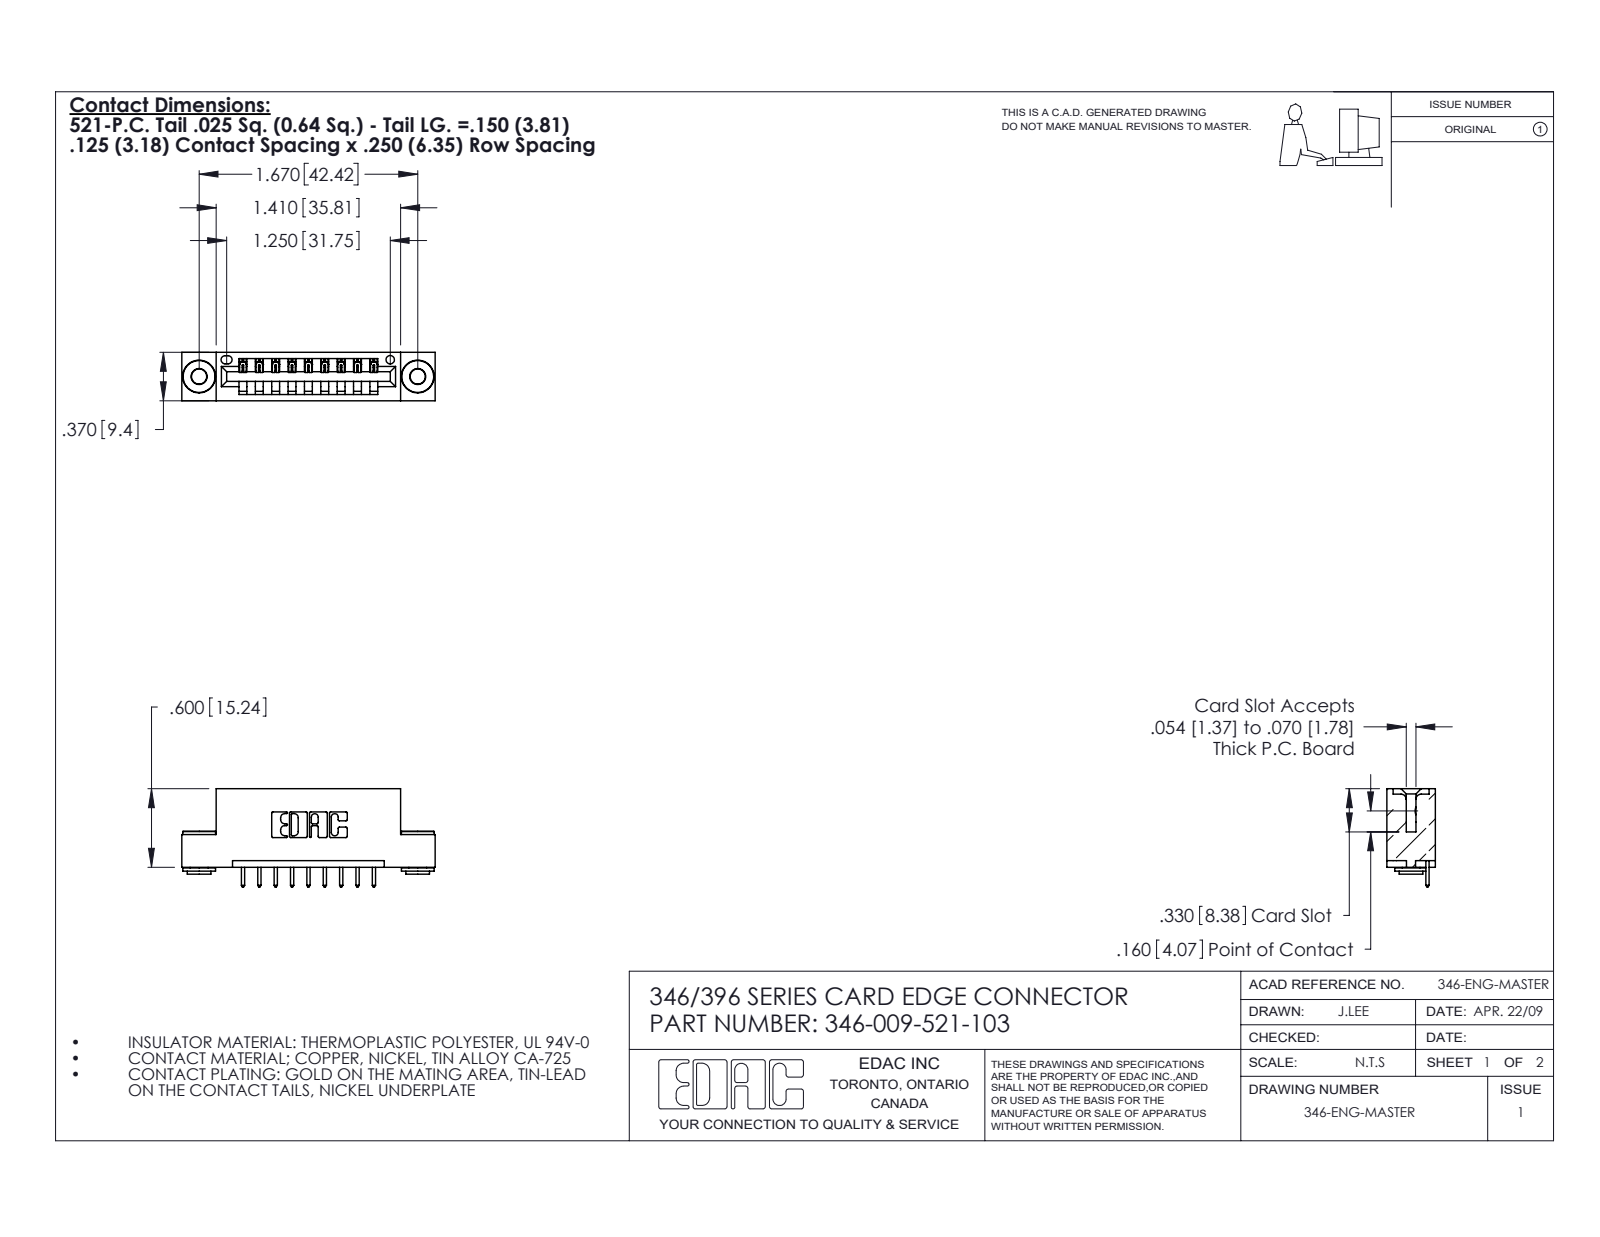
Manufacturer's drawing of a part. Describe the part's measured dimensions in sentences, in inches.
The part is named "346-009-521-103; 345-250-002_345-250-002-102; 346 Part_Flush Mounting Lugs - 0.156 Dia-TH; 345-292-001_345-293-121". Its 3-D file was written by "SolidWorks 2020 (CONFIG_CONTROL_DESIGN)". It is 12 solids with 696 faces: 460 planar, 228 cylindrical and 8 other. Overall it measures 1.935 by 0.75 by 0.37 inches. Its volume is 0.272 cubic inches and its surface area 8.307 square inches. Round holes: 2 of diameter 0.116, 2 of diameter 0.156, 1 of diameter 0.064. Round bosses or shafts: 2 of diameter 0.25, 2 of diameter 0.18, 2 of diameter 0.136. Partial cylindrical surfaces (rounded edges, fillets, slot ends): 22 of radius 0.01, 18 of radius 0.006, 18 of radius 0.01, 6 of radius 0.007, 6 of radius 0.031, 3 of radius 0.026, 2 of radius 0.031, 2 of radius 0.04. The main face-to-face distances are 0.25, 0.37, 0.048, 0.322, 0.025, 0.148, 0.222, 0.1, 0.174, 0.072. The hole center spacings are 0.246, 1.465, 1.67.
